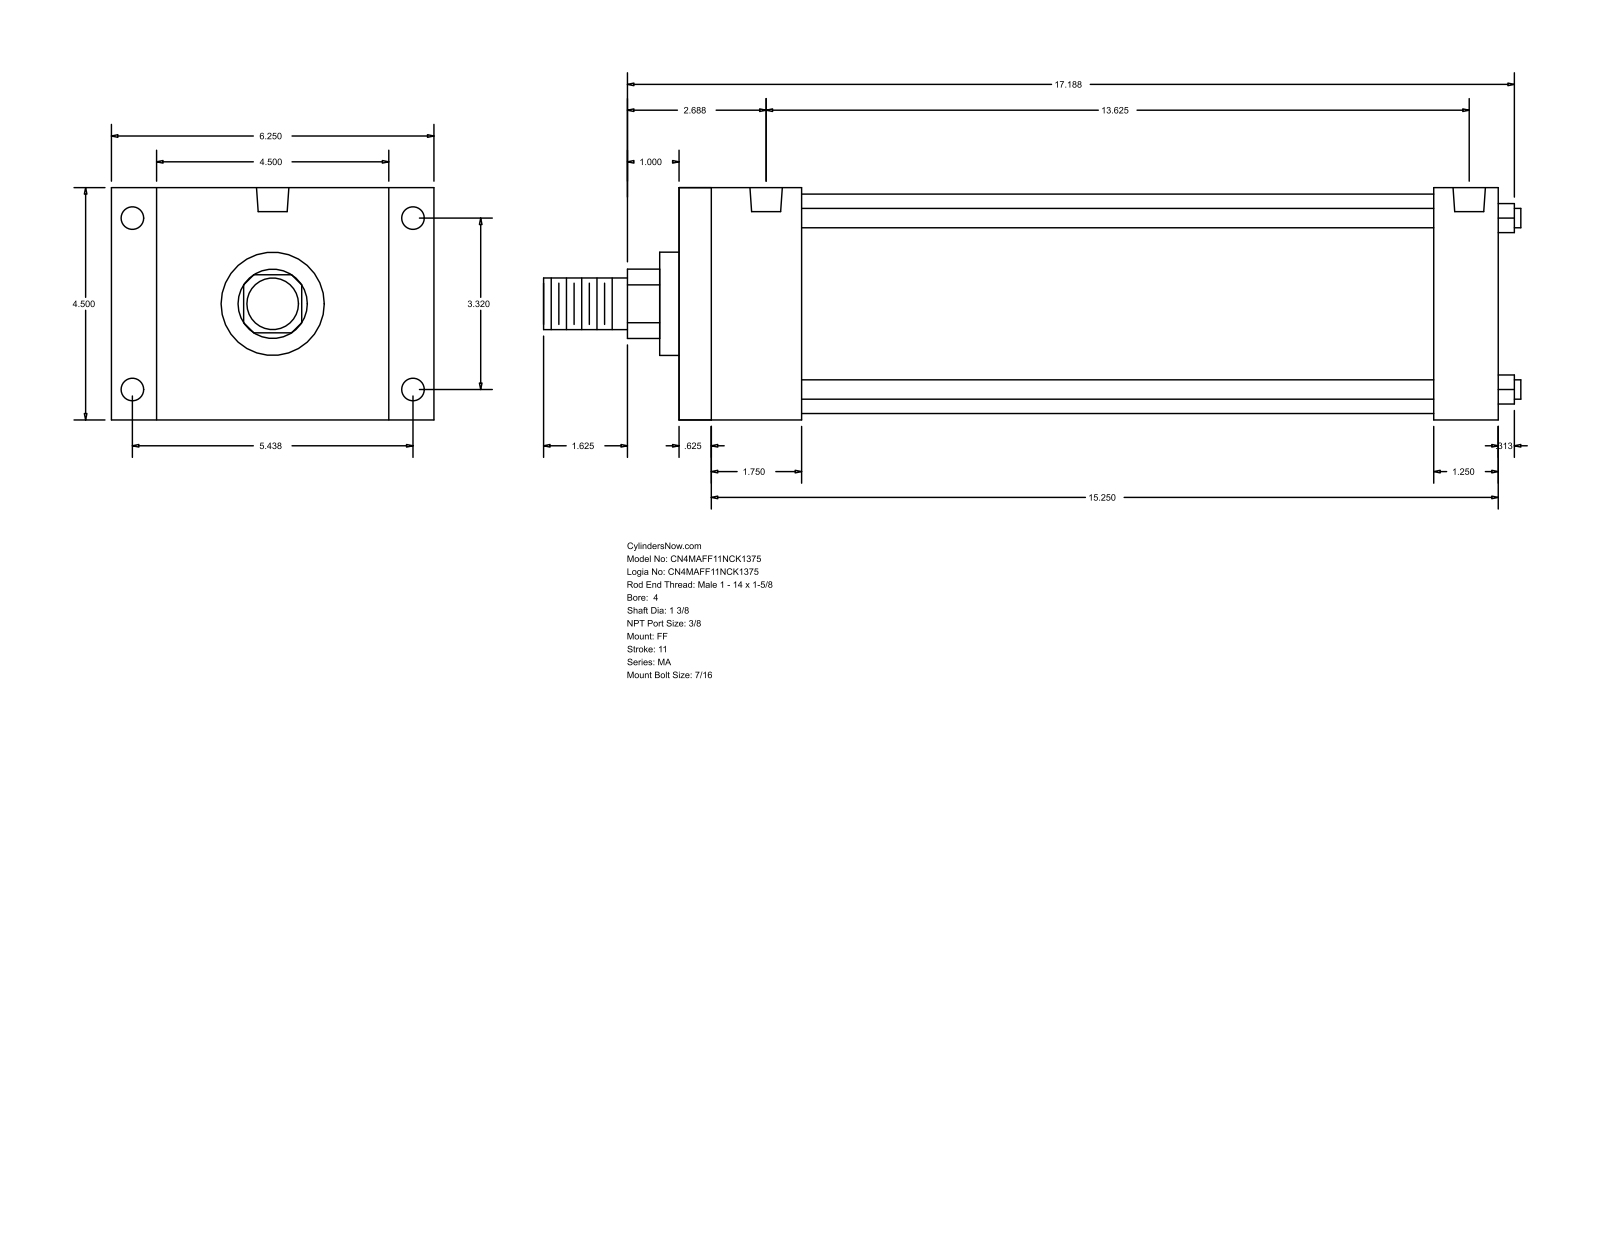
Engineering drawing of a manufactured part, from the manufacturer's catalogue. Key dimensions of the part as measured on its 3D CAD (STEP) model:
Part name (STEP PRODUCT): MA_FF__0400_1.375
STEP written by: GSSL Pune (CONFIG_CONTROL_DESIGN)
Units: millimetres
Bodies: 0 solids, 92 faces (64 planar, 28 cylindrical, 0 other)
Overall size (bounding box): 481.01 × 158.75 × 114.3
Round holes (diameter × count): ⌀11.11 ×8, ⌀15.93 ×2
Round bosses / shafts (diameter × count): ⌀9.53 ×4, ⌀107.95 ×1, ⌀50.8 ×1, ⌀34.92 ×1, ⌀25.4 ×1
Partial cylindrical surfaces — rounded edges, fillets, slot ends (radius × count): R17.06 ×1
Main face-to-face distances: 114.3, 403.22, 15.87, 387.35, 22.23, 136.53, 371.48, 355.61, 31.74, 60.32
Hole centre spacings: 4.77, 84.32, 138.12, 161.82, 336.54, 341.31, 346.08
